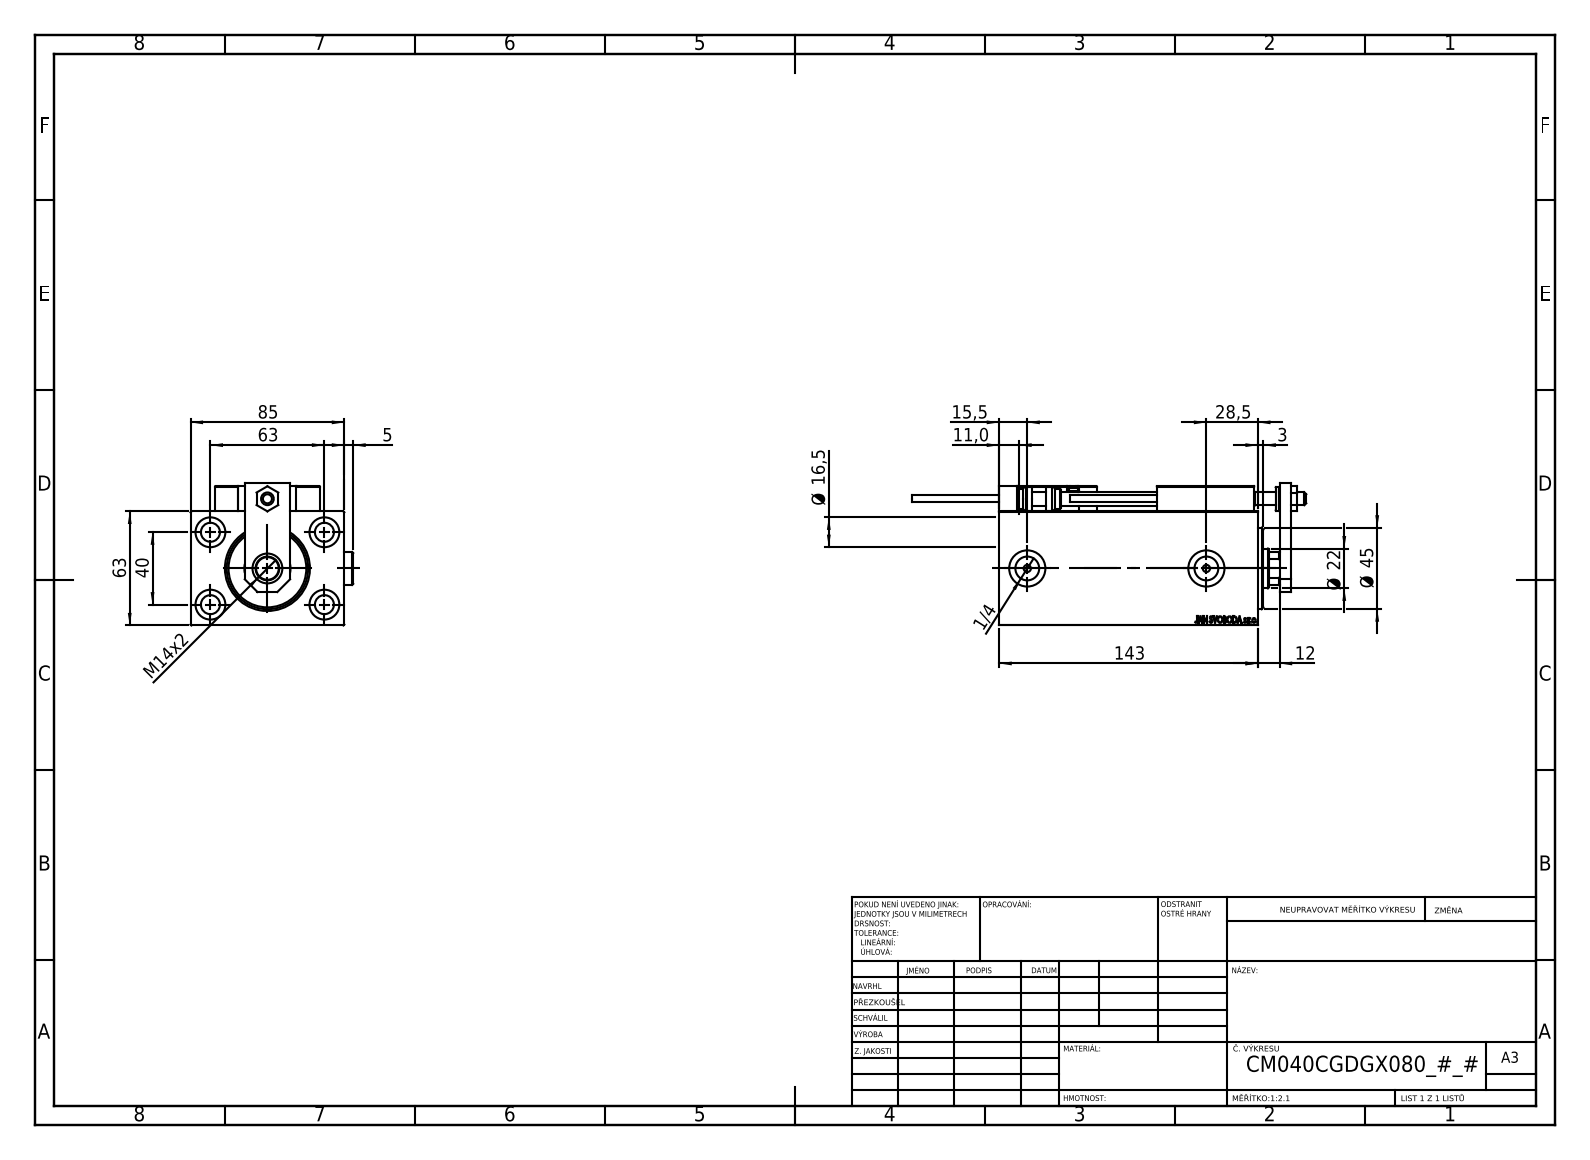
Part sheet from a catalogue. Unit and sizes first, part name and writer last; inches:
Units: inches
Overall size (bounding box): 8.571 × 3.539 × 3.091
Round holes (diameter × count): ⌀0.157 ×6, ⌀0.315 ×5, ⌀0.65 ×5, ⌀0.126 ×4, ⌀0.413 ×4, ⌀0.197 ×2, ⌀0.518 ×2, ⌀0.787 ×2, ⌀0.276 ×1, ⌀0.492 ×1, ⌀0.866 ×1, ⌀1.004 ×1
Round bosses / shafts (diameter × count): ⌀0.709 ×2, ⌀0.197 ×2, ⌀0.15 ×2, ⌀0.512 ×1, ⌀0.433 ×1
Partial cylindrical surfaces — rounded edges, fillets, slot ends (radius × count): R0.012 ×30, R0.118 ×2, R0.413 ×1
Main face-to-face distances: 2.48, 3.346, 0.472, 5.157, 5.63, 0.551, 3.031, 0.591, 0.709, 1.181
Hole centre spacings: 1.469, 0.448, 0.787, 1.165, 1.169, 1.42, 1.438, 1.575
Volume: 41.85 in³ · Surface area: 217.6 in²
Bodies: 25 solids, 1336 faces (594 planar, 204 cylindrical, 538 other)
Part name (STEP PRODUCT): ZARAZKA; NUT_D12; SWITCH DIM B,W; ALLEN BOLT D5 (+7 more)
STEP written by: SolidWorks 2019 (CONFIG_CONTROL_DESIGN)
